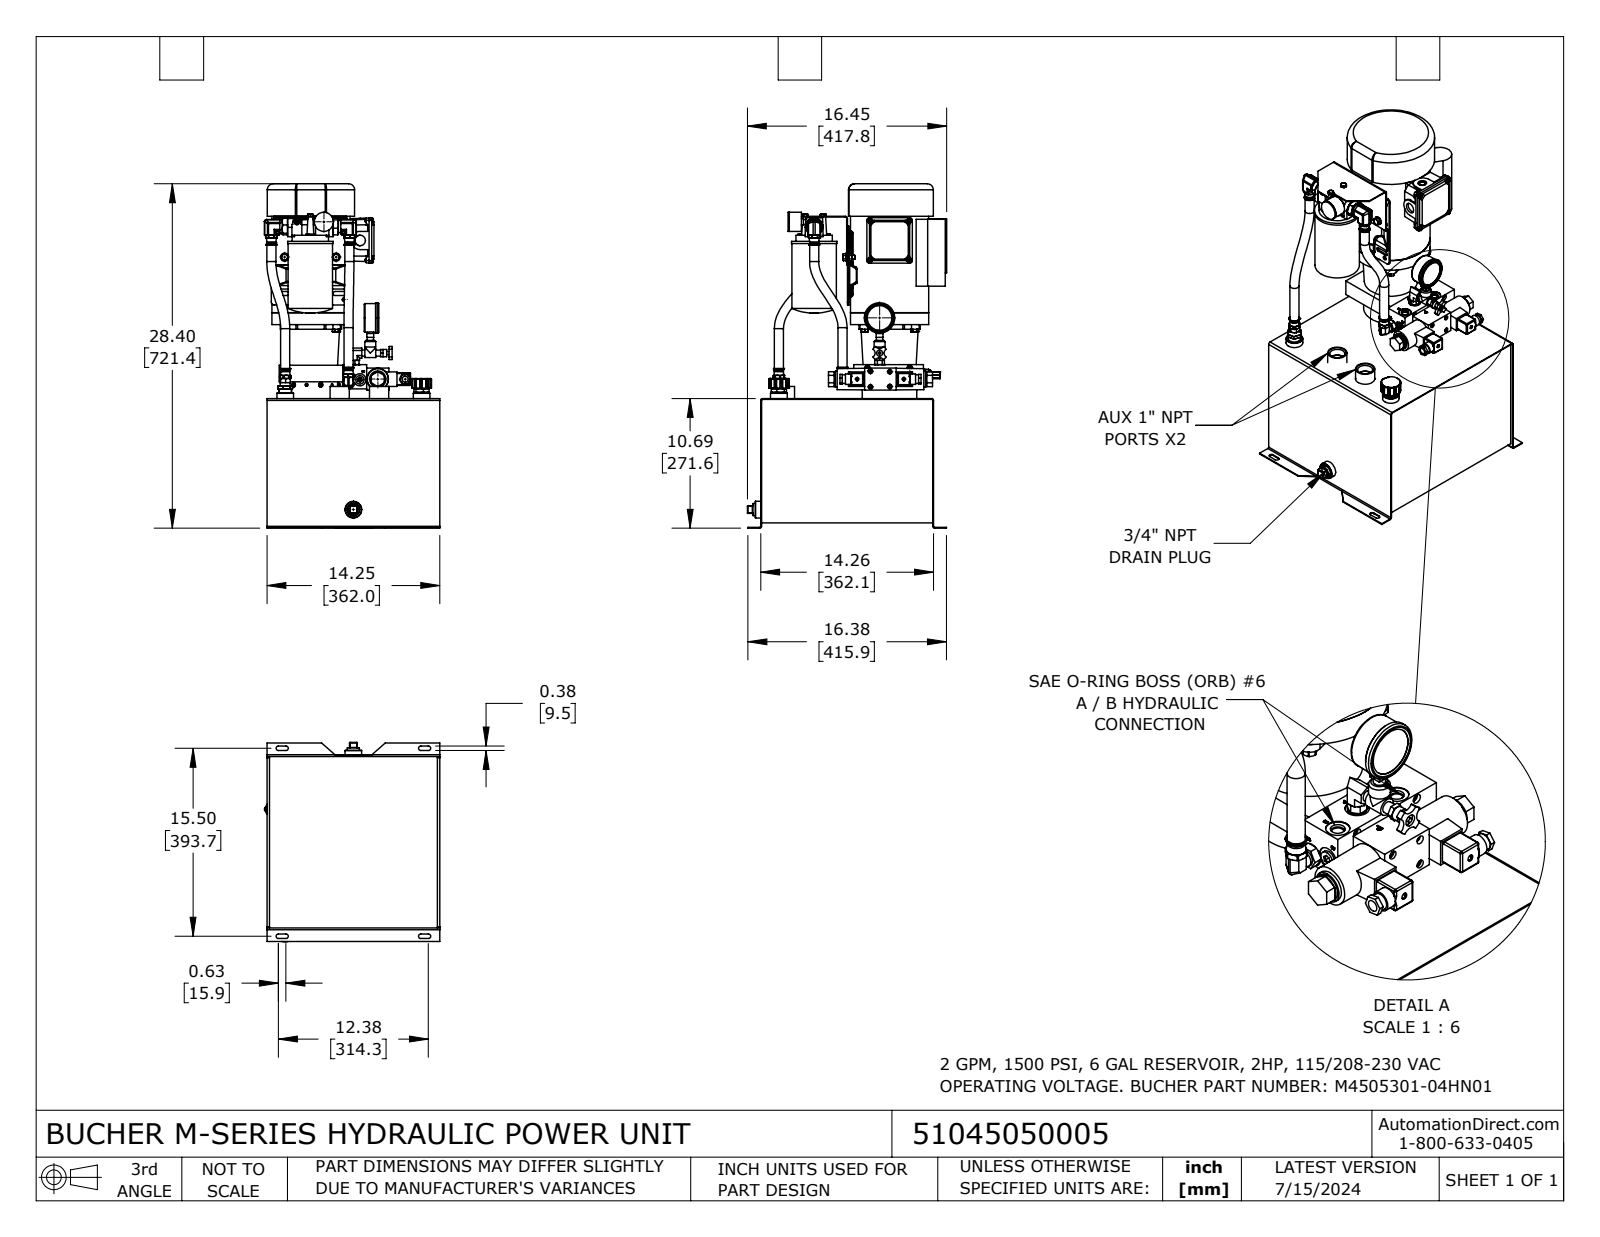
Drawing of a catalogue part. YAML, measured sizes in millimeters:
part_name: "51045050005"
step_written_by: "SolidWorks 2023 (CONFIG_CONTROL_DESIGN)"
units: millimeters
bodies: {solids: 70, faces: 3827, planar: 1691, cylindrical: 1157, other: 979}
overall_size: [721.4, 417.8, 367.5]
volume: 12700000
surface_area: 2346000
round_holes:
  - {diameter: 6.4, count: 9}
  - {diameter: 25.4, count: 9}
  - {diameter: 6.5, count: 8}
  - {diameter: 11.9, count: 8}
  - {diameter: 13, count: 8}
  - {diameter: 5.7, count: 6}
  - {diameter: 8.6, count: 6}
  - {diameter: 12.7, count: 6}
  - {diameter: 3.5, count: 5}
  - {diameter: 7.1, count: 5}
  - {diameter: 8, count: 5}
  - {diameter: 4.3, count: 4}
round_bosses_or_shafts:
  - {diameter: 6.2, count: 7}
  - {diameter: 9.3, count: 6}
  - {diameter: 4.7, count: 6}
  - {diameter: 22.9, count: 5}
  - {diameter: 19.1, count: 5}
  - {diameter: 18.7, count: 4}
  - {diameter: 17.3, count: 4}
  - {diameter: 11.7, count: 4}
partial_cylinders:
  - {radius: 0.6, count: 24}
  - {radius: 1, count: 24}
  - {radius: 1.3, count: 24}
  - {radius: 5, count: 24}
  - {radius: 0.5, count: 20}
  - {radius: 1.8, count: 14}
  - {radius: 8, count: 14}
  - {radius: 3, count: 13}
face_to_face_distances: [1.7, 3.2, 360.5, 260.4, 257.2, 255.5, 258.7, 362.1, 351.8, 358.8]
hole_center_spacings: [40, 53.3, 111.3, 45.2, 56.6, 64, 74.6, 83]
